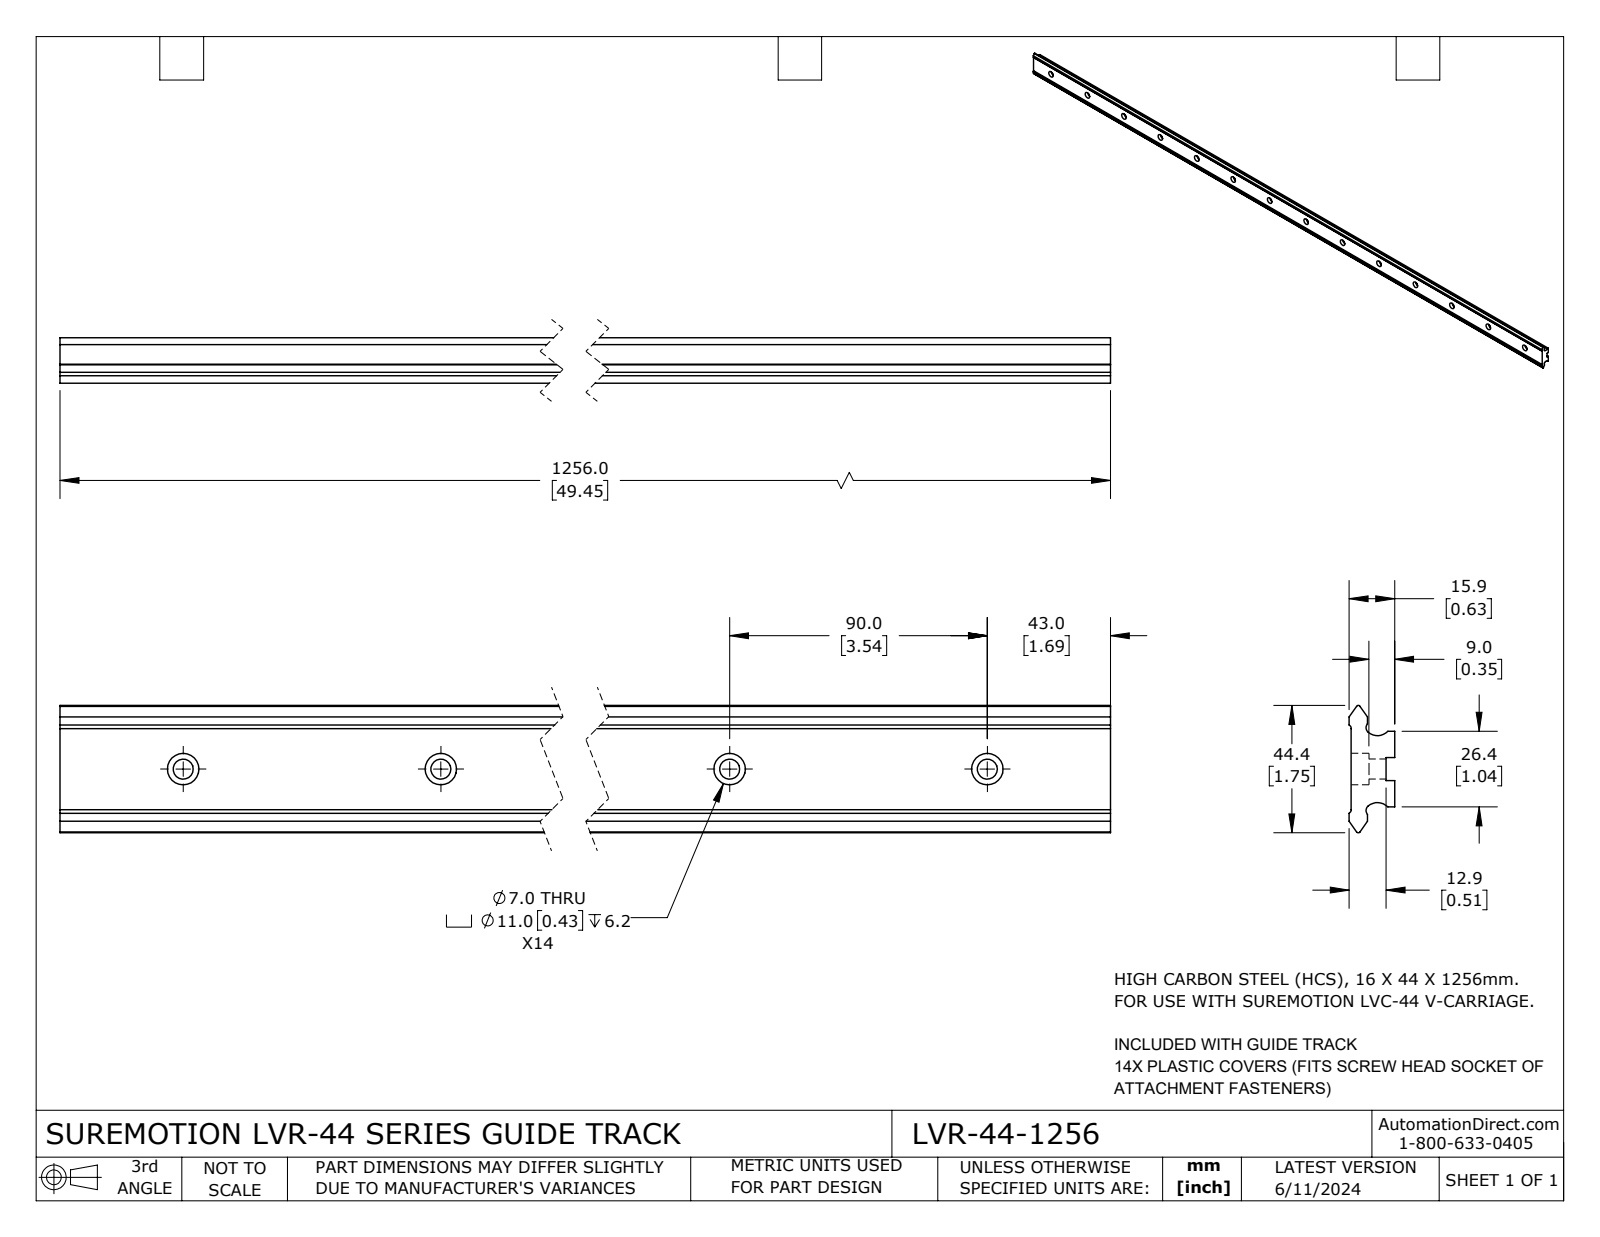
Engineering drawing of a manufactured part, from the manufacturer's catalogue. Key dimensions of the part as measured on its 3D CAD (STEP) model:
Part name (STEP PRODUCT): LVR-44-1256
STEP written by: SolidWorks 2023 (CONFIG_CONTROL_DESIGN)
Units: inches
Bodies: 1 solid, 98 faces (32 planar, 66 cylindrical, 0 other)
Overall size (bounding box): 49.449 × 1.75 × 0.626
Volume: 33.86 in³ · Surface area: 243.8 in²
Round holes (diameter × count): ⌀0.276 ×14, ⌀0.433 ×14
Partial cylindrical surfaces — rounded edges, fillets, slot ends (radius × count): R0.03 ×2, R0.059 ×2, R0.084 ×2, R0.196 ×2
Main face-to-face distances: 0.598, 1.03, 0.118, 0.48, 0.626, 0.508, 0.028, 0.362, 0.677, 0.373
Hole centre spacings: 3.543, 7.087, 10.63, 14.173, 17.717, 21.26, 24.803, 28.346
